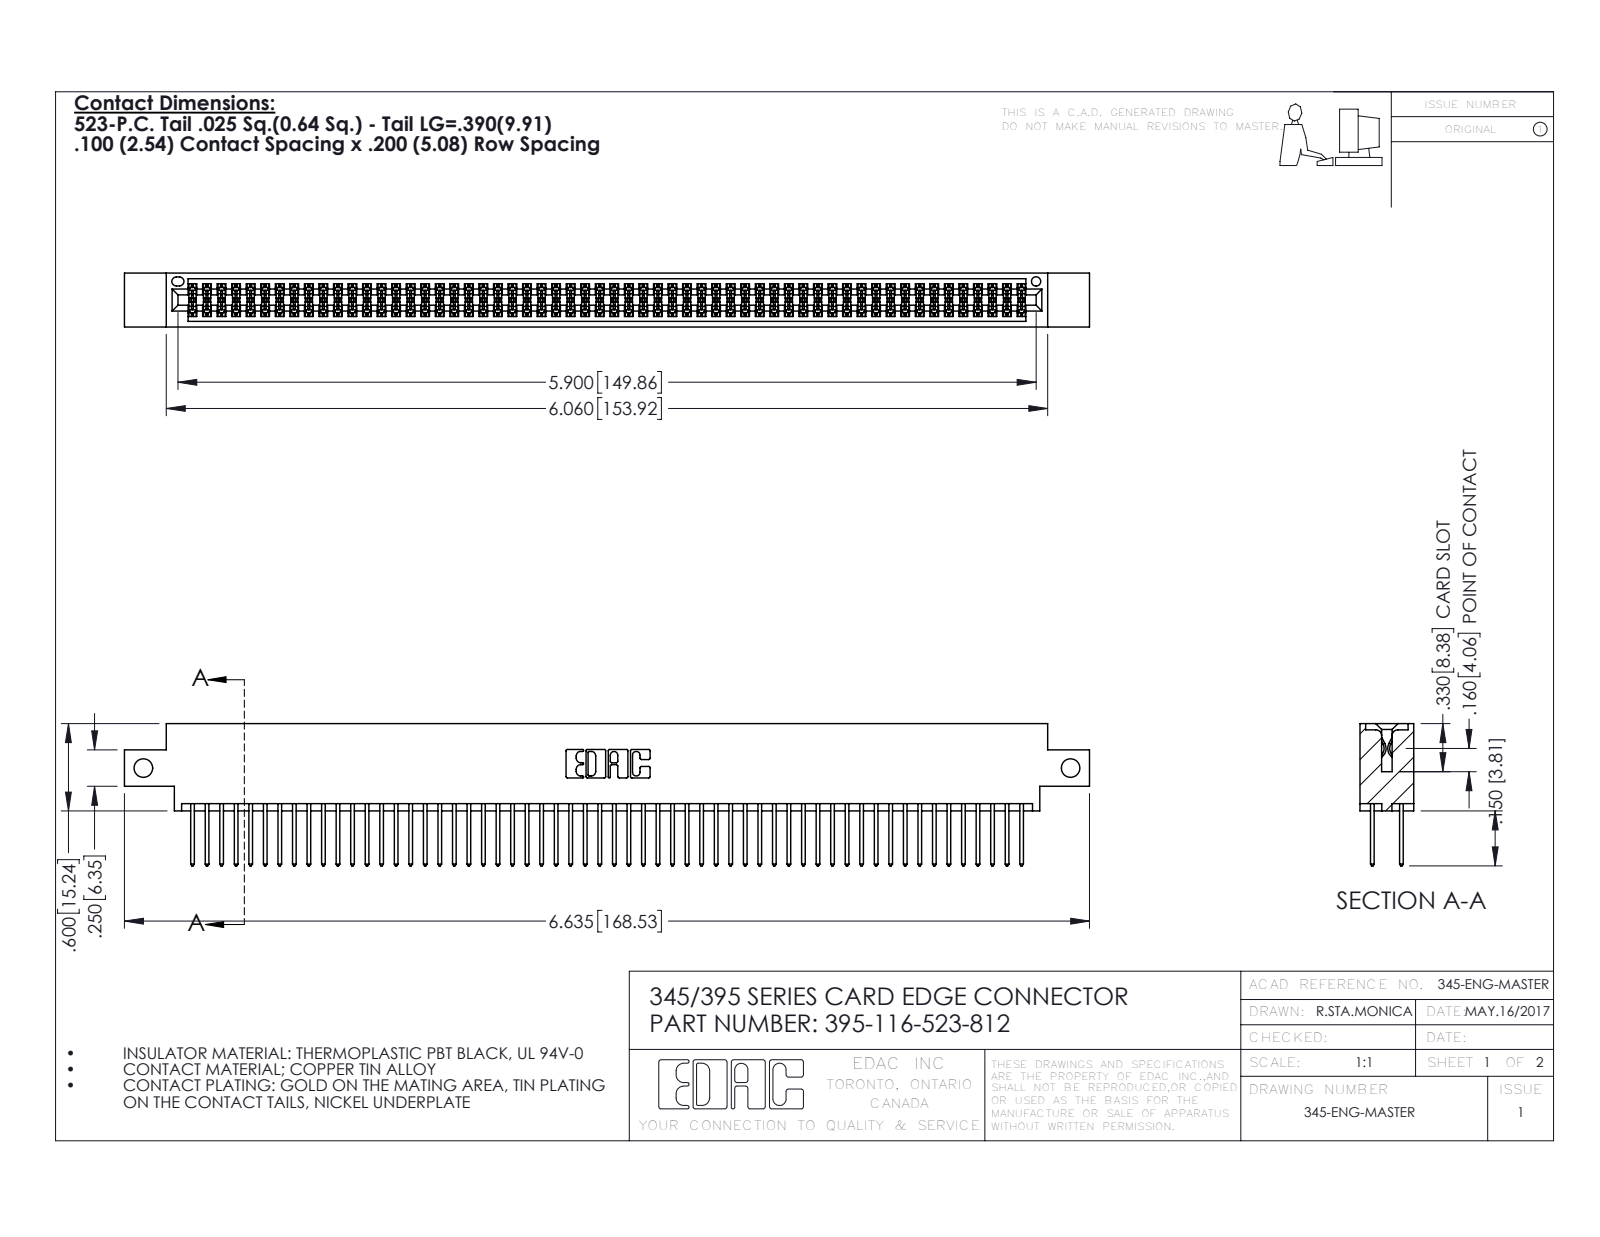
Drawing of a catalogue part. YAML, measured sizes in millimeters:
part_name: "345 Part_0.170 Offset - Side Mount; 345-292-001_345-293-123; 395-116-523-812"
step_written_by: "SolidWorks 2016 (CONFIG_CONTROL_DESIGN)"
units: millimeters
bodies: {solids: 117, faces: 5930, planar: 3912, cylindrical: 2018, other: 0}
overall_size: [168.5, 24.8, 9.4]
volume: 16550
surface_area: 25860
round_holes:
  - {diameter: 3.3, count: 2}
  - {diameter: 1.6, count: 1}
partial_cylinders:
  - {radius: 0.2, count: 174}
  - {radius: 0.3, count: 116}
  - {radius: 0.3, count: 22}
  - {radius: 0.2, count: 6}
  - {radius: 0.8, count: 6}
  - {radius: 0.7, count: 3}
  - {radius: 0.4, count: 2}
  - {radius: 0.5, count: 2}
face_to_face_distances: [7.6, 1.8, 5.1, 2.5, 6.9, 0.6, 9.4, 5.7, 4.4, 3.8]
hole_center_spacings: [161.9]
